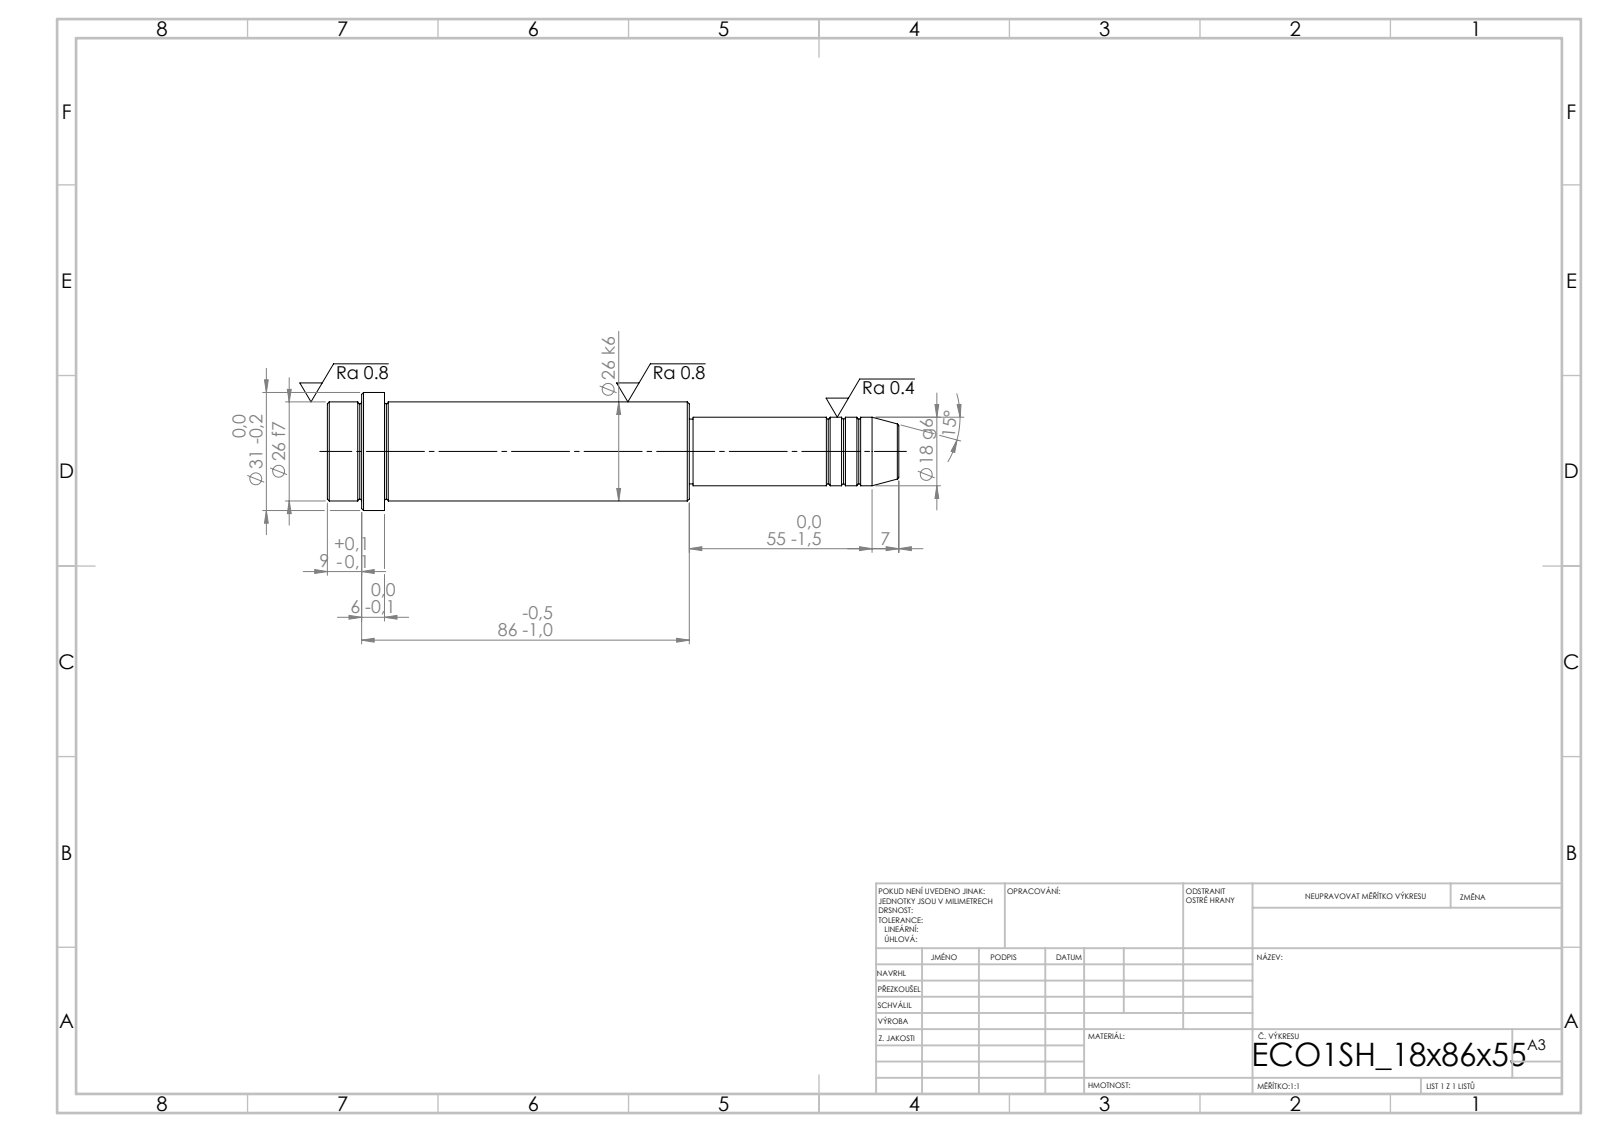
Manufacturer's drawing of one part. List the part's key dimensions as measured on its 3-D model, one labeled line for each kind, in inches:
STEP written by: SolidWorks 2019 (CONFIG_CONTROL_DESIGN)
Units: inches
Bodies: 1 solid, 52 faces (6 planar, 16 cylindrical, 30 other)
Overall size (bounding box): 5.906 × 1.22 × 1.22
Volume: 3.981 in³ · Surface area: 19.37 in²
Round bosses / shafts (diameter × count): ⌀1.22 ×1, ⌀1.024 ×1, ⌀0.709 ×1, ⌀0.669 ×1
Main face-to-face distances: 3.74, 3.15, 0.591, 3.386, 0.236, 0.354, 2.165, 5.315, 5.551, 5.906
